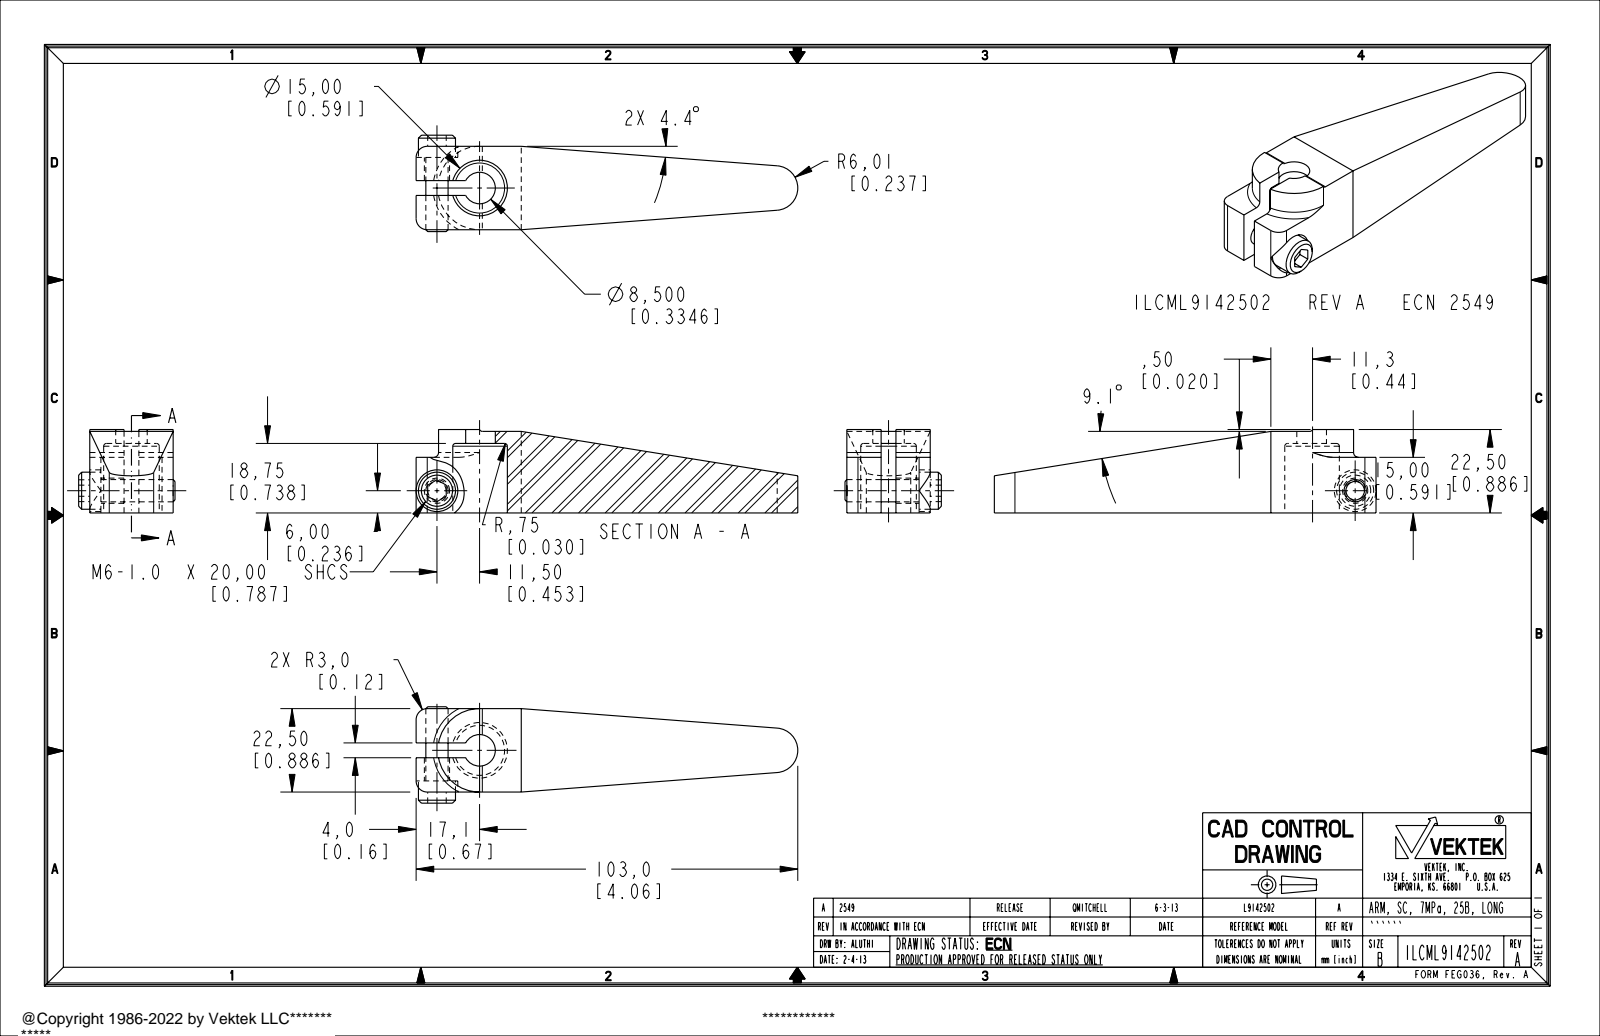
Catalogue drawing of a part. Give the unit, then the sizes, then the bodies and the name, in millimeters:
Units: millimetres
Overall size (bounding box): 103 × 26 × 22.5
Round holes (diameter × count): ⌀6.8 ×1, ⌀8.5 ×1, ⌀11.25 ×1, ⌀15 ×1
Round bosses / shafts (diameter × count): ⌀10 ×1, ⌀6 ×1
Partial cylindrical surfaces — rounded edges, fillets, slot ends (radius × count): R3 ×2, R0.8 ×1, R6.01 ×1, R11.25 ×1
Main face-to-face distances: 22.5, 9.25, 13.25, 22, 0.5, 4, 3.75, 15, 7, 7.5
Volume: 29 530 mm³ · Surface area: 9 503 mm²
Bodies: 1 solid, 55 faces (27 planar, 21 cylindrical, 7 other)
Part name (STEP PRODUCT): ILCML9142502
STEP written by: PRO/ENGINEER BY PARAMETRIC TECHNOLOGY CORPORATION, 2007460 (AUTOMOTIVE_DESIGN_CC2)
